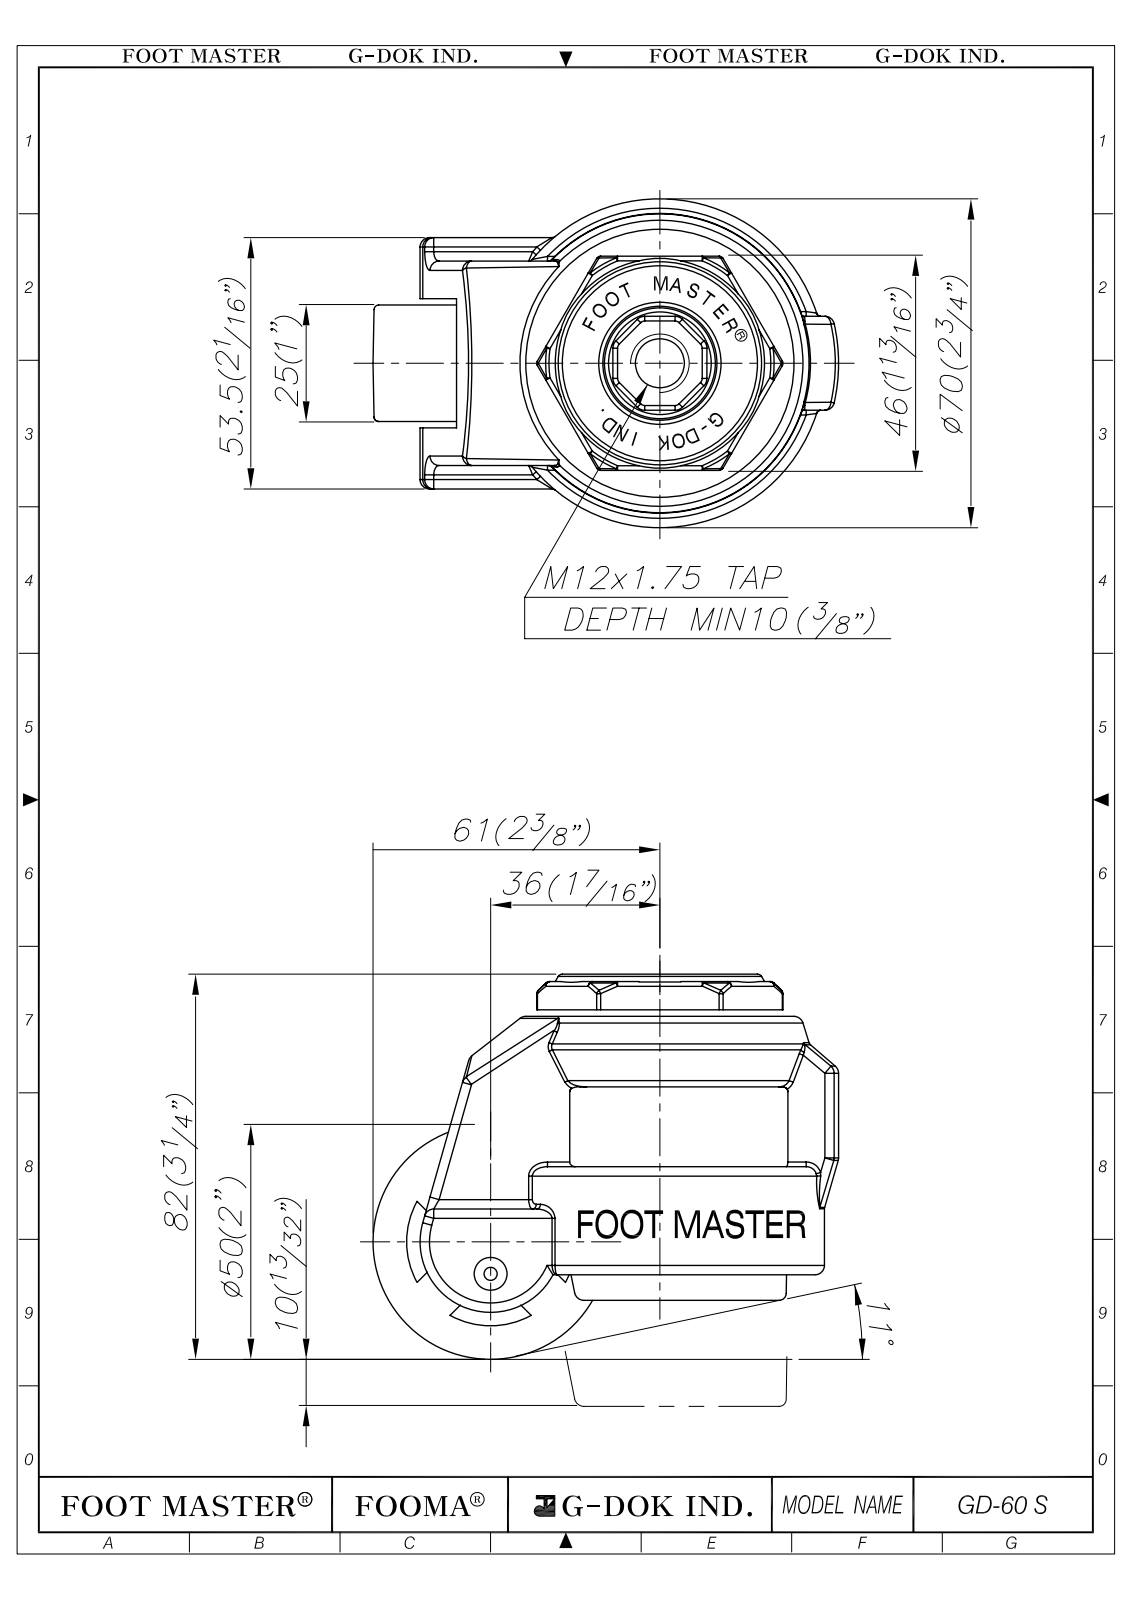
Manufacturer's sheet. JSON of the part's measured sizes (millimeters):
{"part_name": "GD-60S", "step_written_by": "Autodesk Inventor 2009 (AUTOMOTIVE_DESIGN)", "units": "millimeters", "bodies": {"solids": 3, "faces": 906, "planar": 411, "cylindrical": 170, "other": 325}, "overall_size": [99, 82.6, 70], "volume_mm3": 213448, "surface_area_mm2": 64397, "round_holes": [[7, 2], [4.1, 1], [8.4, 1], [10, 1], [10.5, 1], [25, 1], [25.5, 1], [35, 1], [39.4, 1], [58, 1]], "round_bosses_or_shafts": [[3, 3], [20, 2], [39, 1], [27, 1], [21, 1], [10, 1], [8, 1], [1, 1]], "partial_cylinders_radius": [[1, 24], [2, 15], [0.5, 12], [5.1, 1], [15, 1], [18, 1], [22.2, 1], [22.5, 1]], "face_to_face_distances": [5, 1, 15, 1.8, 10, 1.25, 26.25, 8, 27.5, 11], "hole_center_spacings": [1.6, 5.2, 6.8]}
